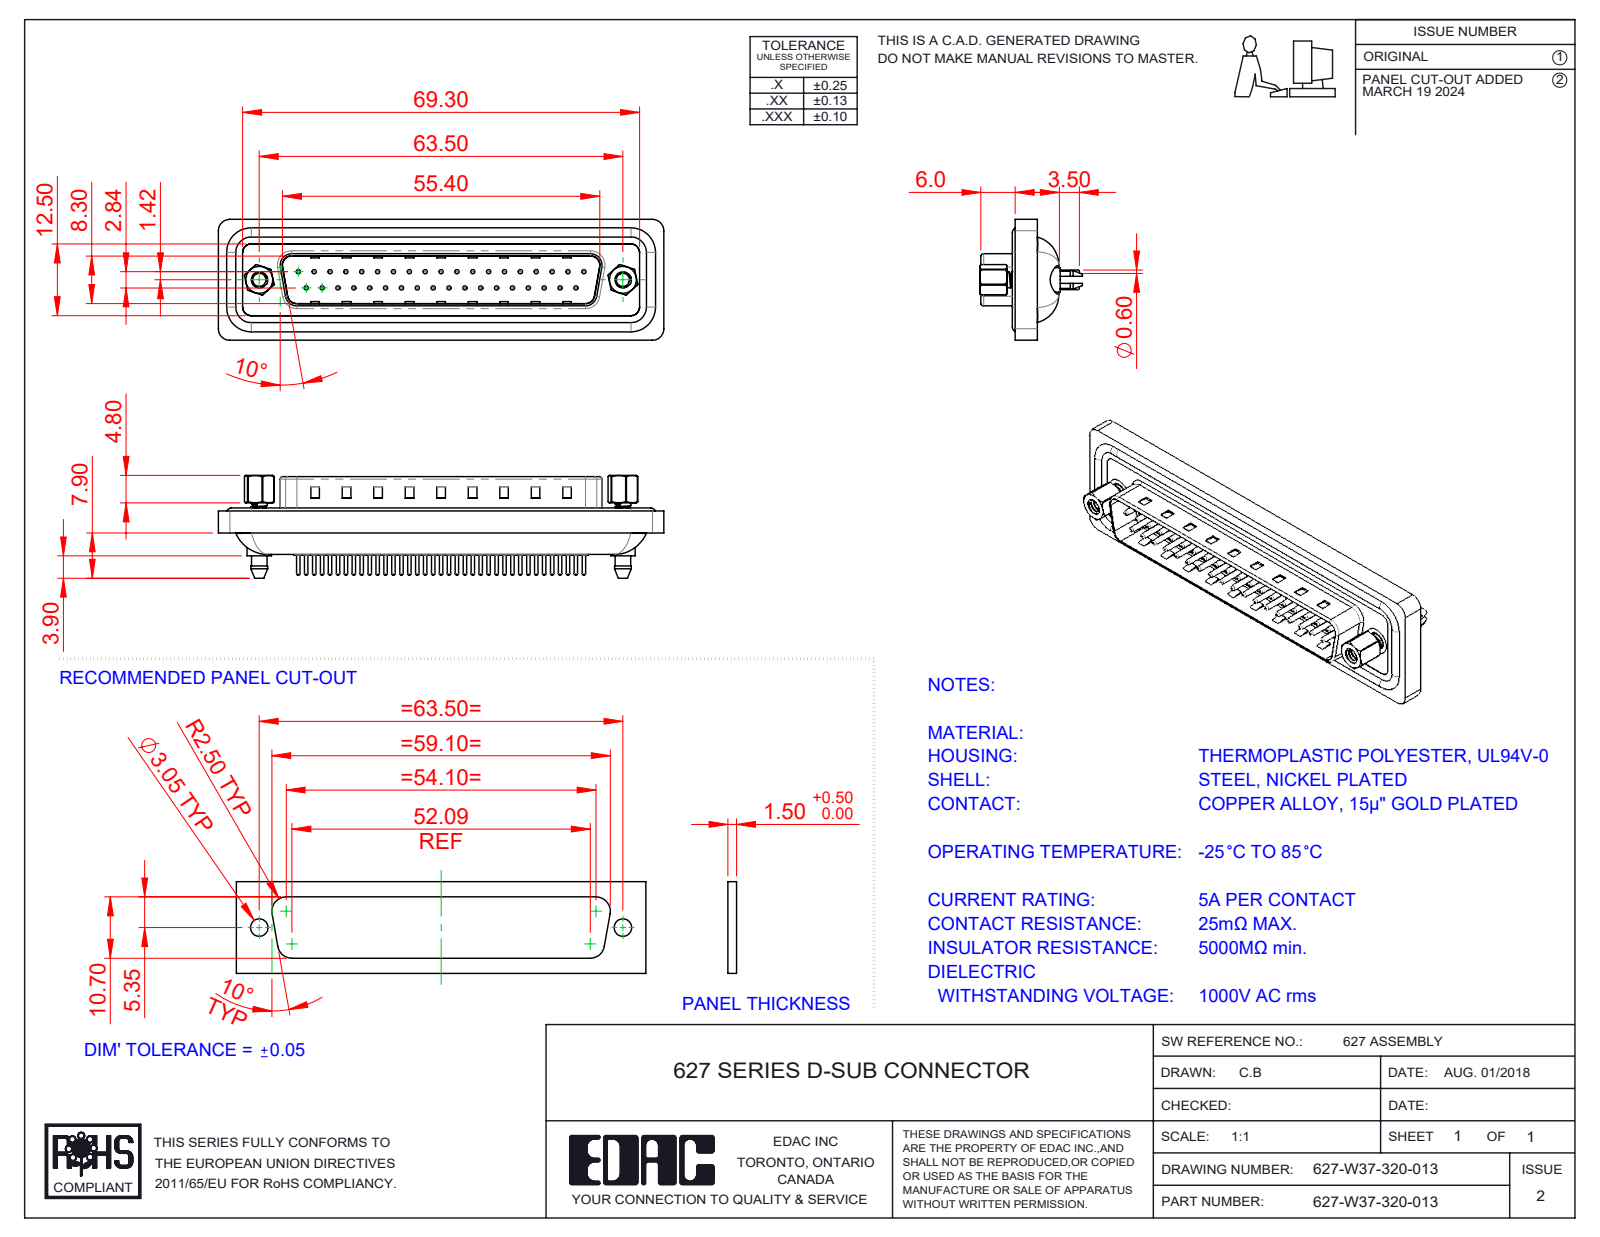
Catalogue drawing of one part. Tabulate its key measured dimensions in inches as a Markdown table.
| quantity | value |
| --- | --- |
| part name | 627W Contact Row 2_20; 627W 4-40 Hex Standoff; 627W Waterproof Housing_37 Contacts BL; 627-W37-320-013 (+4 more) |
| STEP written by | SolidWorks 2023 (CONFIG_CONTROL_DESIGN) |
| units | inches |
| bodies | 45 solids, 2047 faces (510 planar, 848 cylindrical, 689 other) |
| overall size | 3.063 × 0.831 × 0.707 |
| volume | 0.582 in³ |
| surface area | 22.85 in² |
| round holes (diameter × count) | 0.03 × 37, 0.059 × 37, 0.063 × 37, 0.079 × 37, 0.089 × 2, 0.09 × 2, 0.157 × 2, 0.189 × 2, 0.197 × 2 |
| round bosses / shafts (diameter × count) | 0.024 × 37, 0.059 × 9, 0.063 × 4, 0.213 × 2, 0.193 × 2, 0.167 × 2, 0.11 × 2 |
| partial cylindrical surfaces (radius × count) | 0.059 × 16, 0.079 × 16, 0.02 × 8, 0.063 × 6, 0.035 × 4, 0.106 × 4, 0.169 × 4, 0.016 × 2 |
| main face-to-face distances | 0.03, 0.016, 0.161, 0.043, 0.108, 0.222, 0.181, 0.608, 0.148, 0.579 |
| hole center spacings | 0.124, 0.109, 0.218, 0.327, 0.198, 0.398, 0.436, 0.503 |
